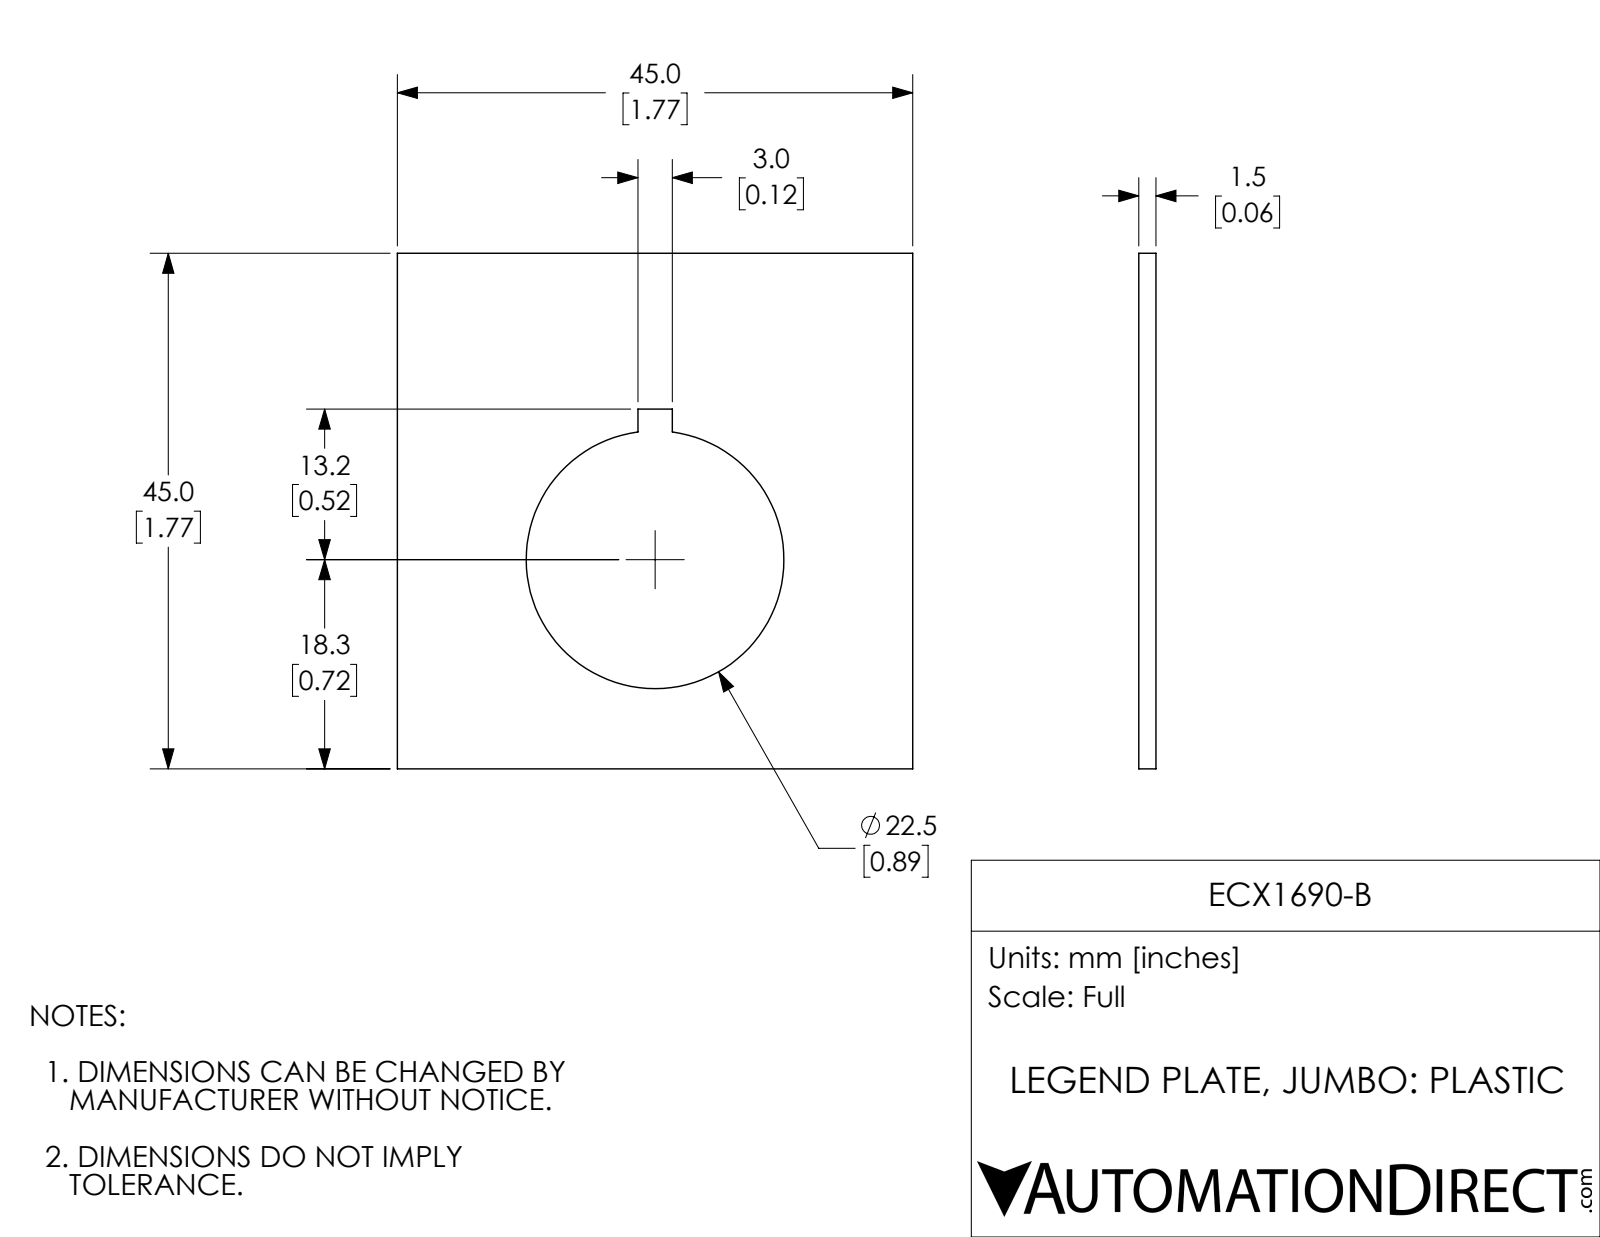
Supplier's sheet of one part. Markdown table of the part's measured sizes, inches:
| quantity | value |
| --- | --- |
| part name | ECX1690-B |
| STEP written by | SolidWorks 2018 (AUTOMOTIVE_DESIGN) |
| units | inches |
| bodies | 1 solid, 12 faces (9 planar, 3 cylindrical, 0 other) |
| overall size | 1.772 × 1.772 × 0.059 |
| volume | 0.148 in³ |
| surface area | 5.619 in² |
| round holes (diameter × count) | 0.886 × 1 |
| main face-to-face distances | 0.059, 1.772, 0.827, 0.945, 1.236, 0.535, 0.118 |
